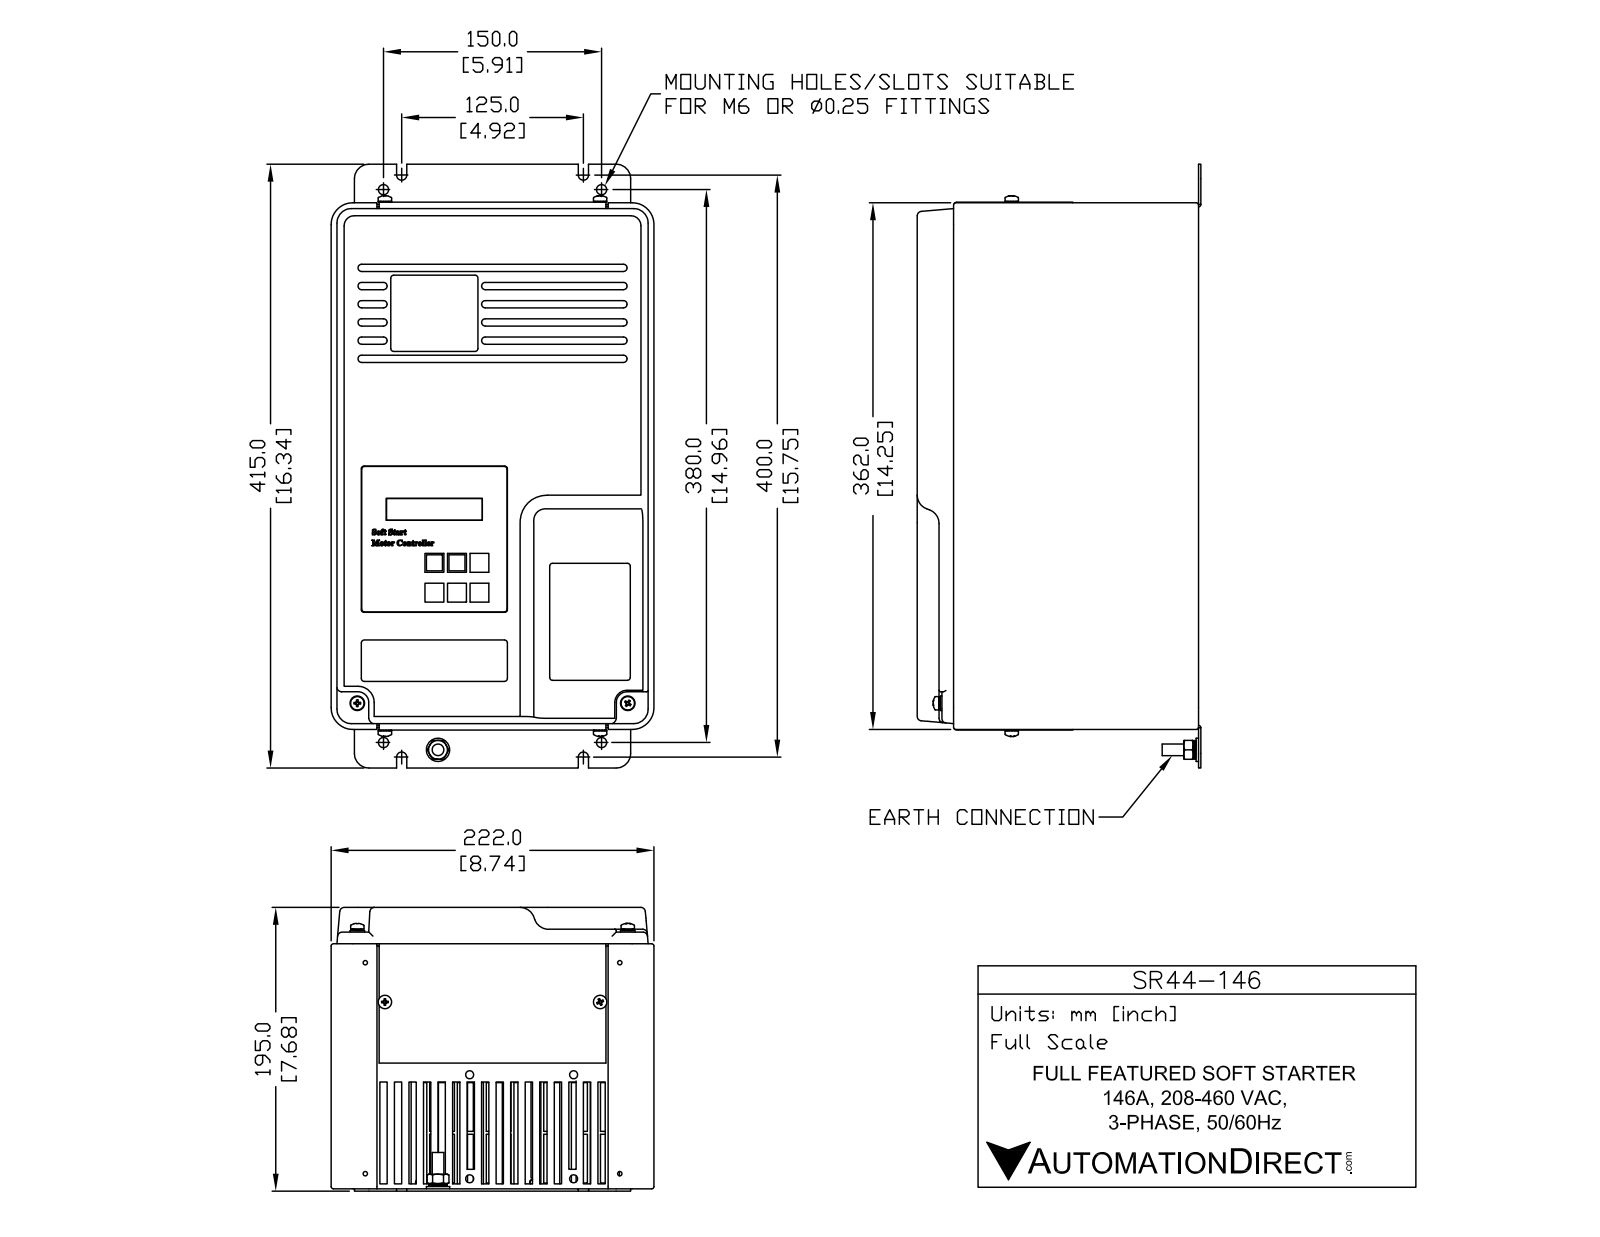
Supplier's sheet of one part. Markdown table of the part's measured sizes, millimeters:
| quantity | value |
| --- | --- |
| part name | SR44-146 |
| STEP written by | SolidWorks 2013 (AUTOMOTIVE_DESIGN) |
| units | millimeters |
| bodies | 1 solid, 768 faces (455 planar, 175 cylindrical, 138 other) |
| overall size | 415 × 222 × 194.7 |
| volume | 8 231 000 mm³ |
| surface area | 711 054 mm² |
| round holes (diameter × count) | 7 × 4 |
| round bosses / shafts (diameter × count) | 10 × 4, 16 × 1, 8 × 1 |
| partial cylindrical surfaces (radius × count) | 2.5 × 30, 2.4 × 28, 2.49 × 12, 1.5 × 11, 3 × 8, 10 × 8, 2 × 6, 3.5 × 4 |
| main face-to-face distances | 10.19, 20.38, 30.57, 40.76, 50.95, 61.14, 71.33, 5.9, 81.52, 216.1 |
| hole center spacings | 150, 380, 408.53 |
